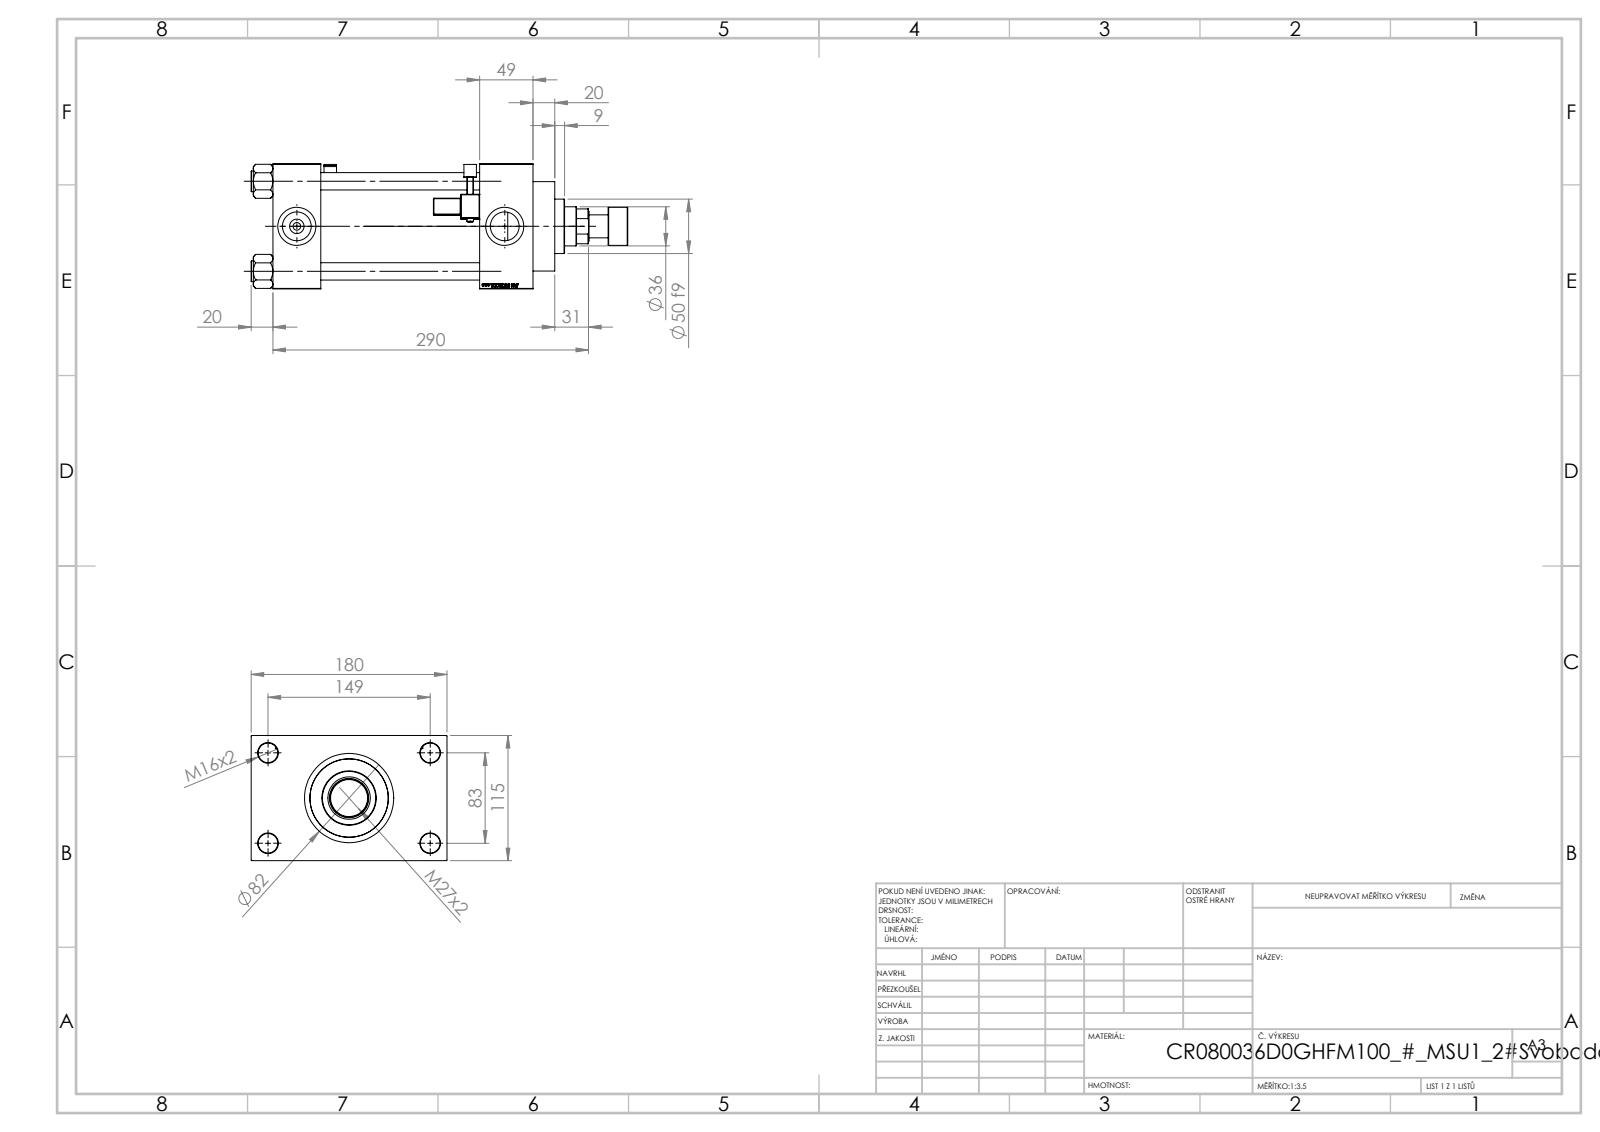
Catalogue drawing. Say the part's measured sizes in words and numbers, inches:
The part is named "V215CR_ROD_END_F; V215CR_D_Body; V215CR_D_TYCINKA; V215CR_VCP_D (+3 more)". Its 3-D file was written by "SolidWorks 2019 (CONFIG_CONTROL_DESIGN)". It is 14 solids with 1319 faces: 607 planar, 152 cylindrical and 560 other. Overall it measures 13.622 by 7.087 by 4.528 inches. Its volume is 137.5 cubic inches and its surface area 591.3 square inches. Round holes: 4 of diameter 0.63, 4 of diameter 0.709, 2 of diameter 0.276, 2 of diameter 1.041, 2 of diameter 1.378, 1 of diameter 1.004, 1 of diameter 1.417, 1 of diameter 1.535, 1 of diameter 2.402, 1 of diameter 2.835, 1 of diameter 3.15. Round bosses or shafts: 4 of diameter 0.748, 2 of diameter 0.236, 1 of diameter 3.386, 1 of diameter 3.228, 1 of diameter 1.969, 1 of diameter 1.378, 1 of diameter 0.827. Partial cylindrical surfaces (rounded edges, fillets, slot ends): 48 of radius 0.02, 2 of radius 0.039, 2 of radius 0.098, 2 of radius 0.157. The main face-to-face distances are 4.528, 5.748, 1.929, 7.677, 1.732, 7.48, 9.409, 1.28, 5.807, 3.937. The hole center spacings are 1.305, 2.302, 3.256, 3.357, 3.513, 4.561, 5.607, 3.268.
